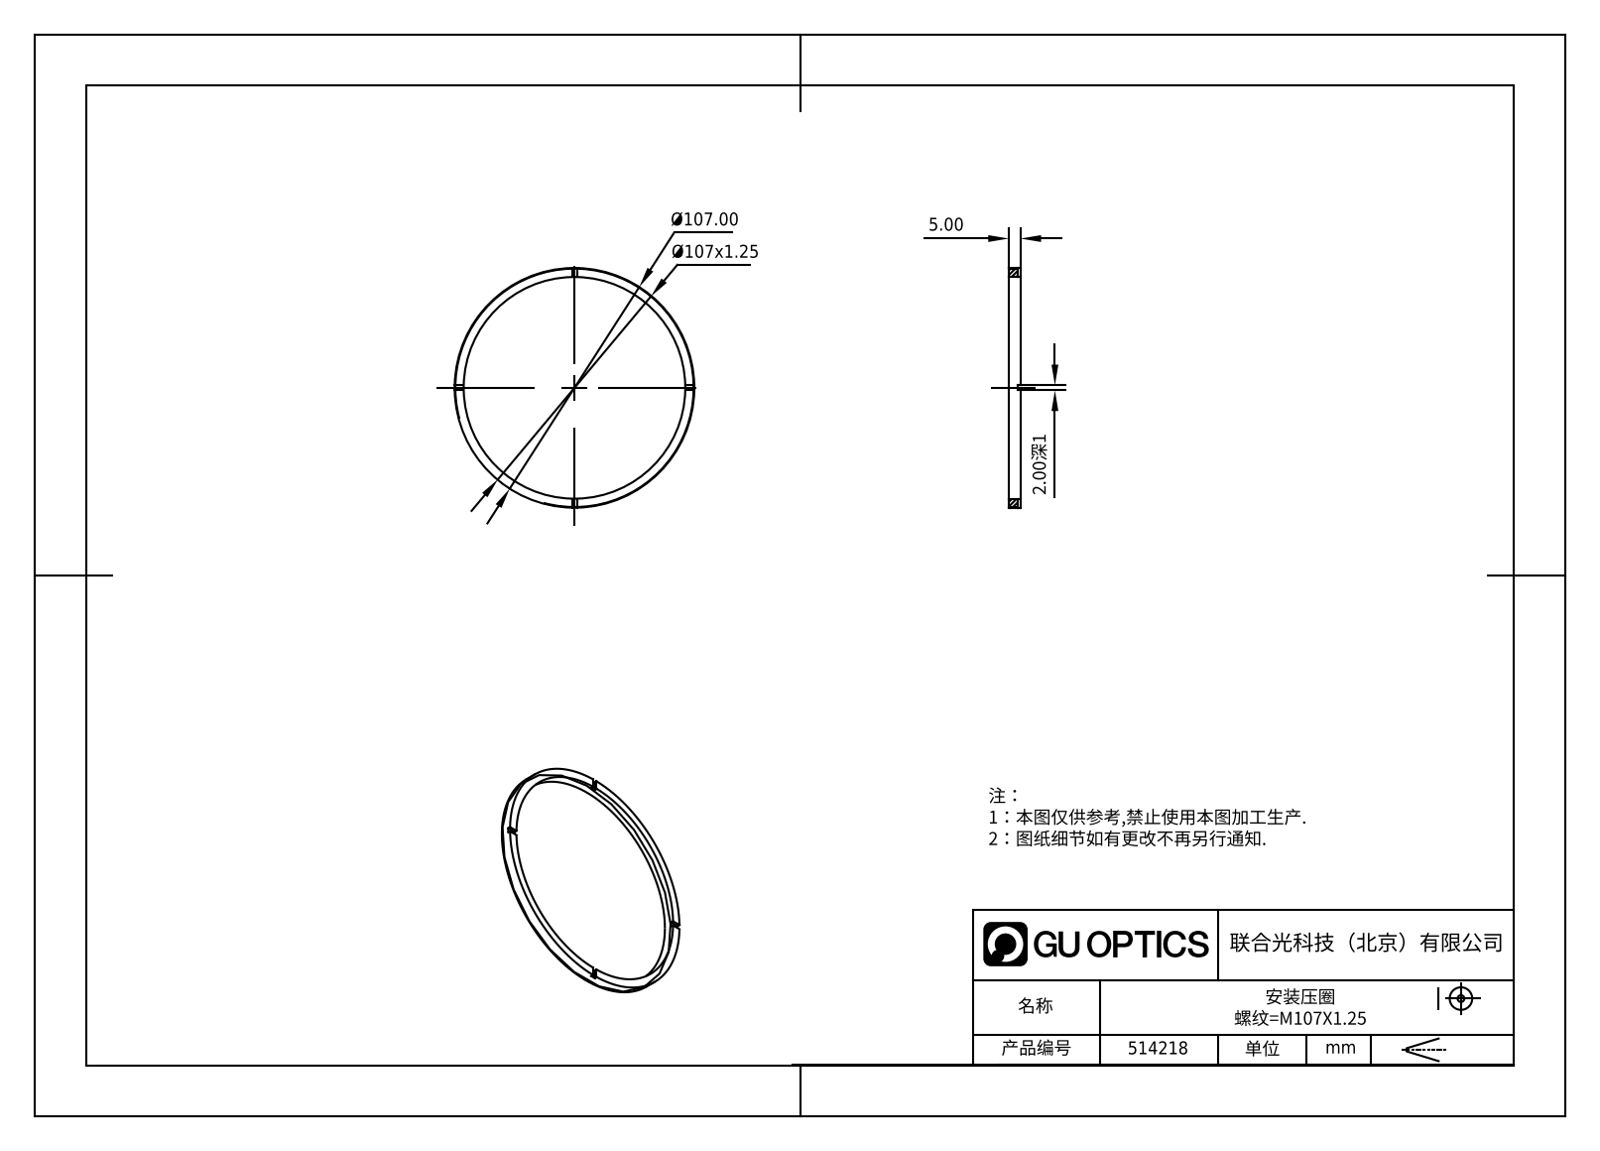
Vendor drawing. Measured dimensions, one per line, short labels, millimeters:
name: 514218
written by: SolidWorks 2020 (CONFIG_CONTROL_DESIGN)
unit: mm
bodies: 1 solid, 21 faces (17 planar, 4 cylindrical, 0 other)
size: 107 × 107 × 5
volume: 6 440 mm³; area: 5 841 mm²
holes: 1× ⌀99
bosses: 1× ⌀107
face distances: 5, 4, 1, 2
